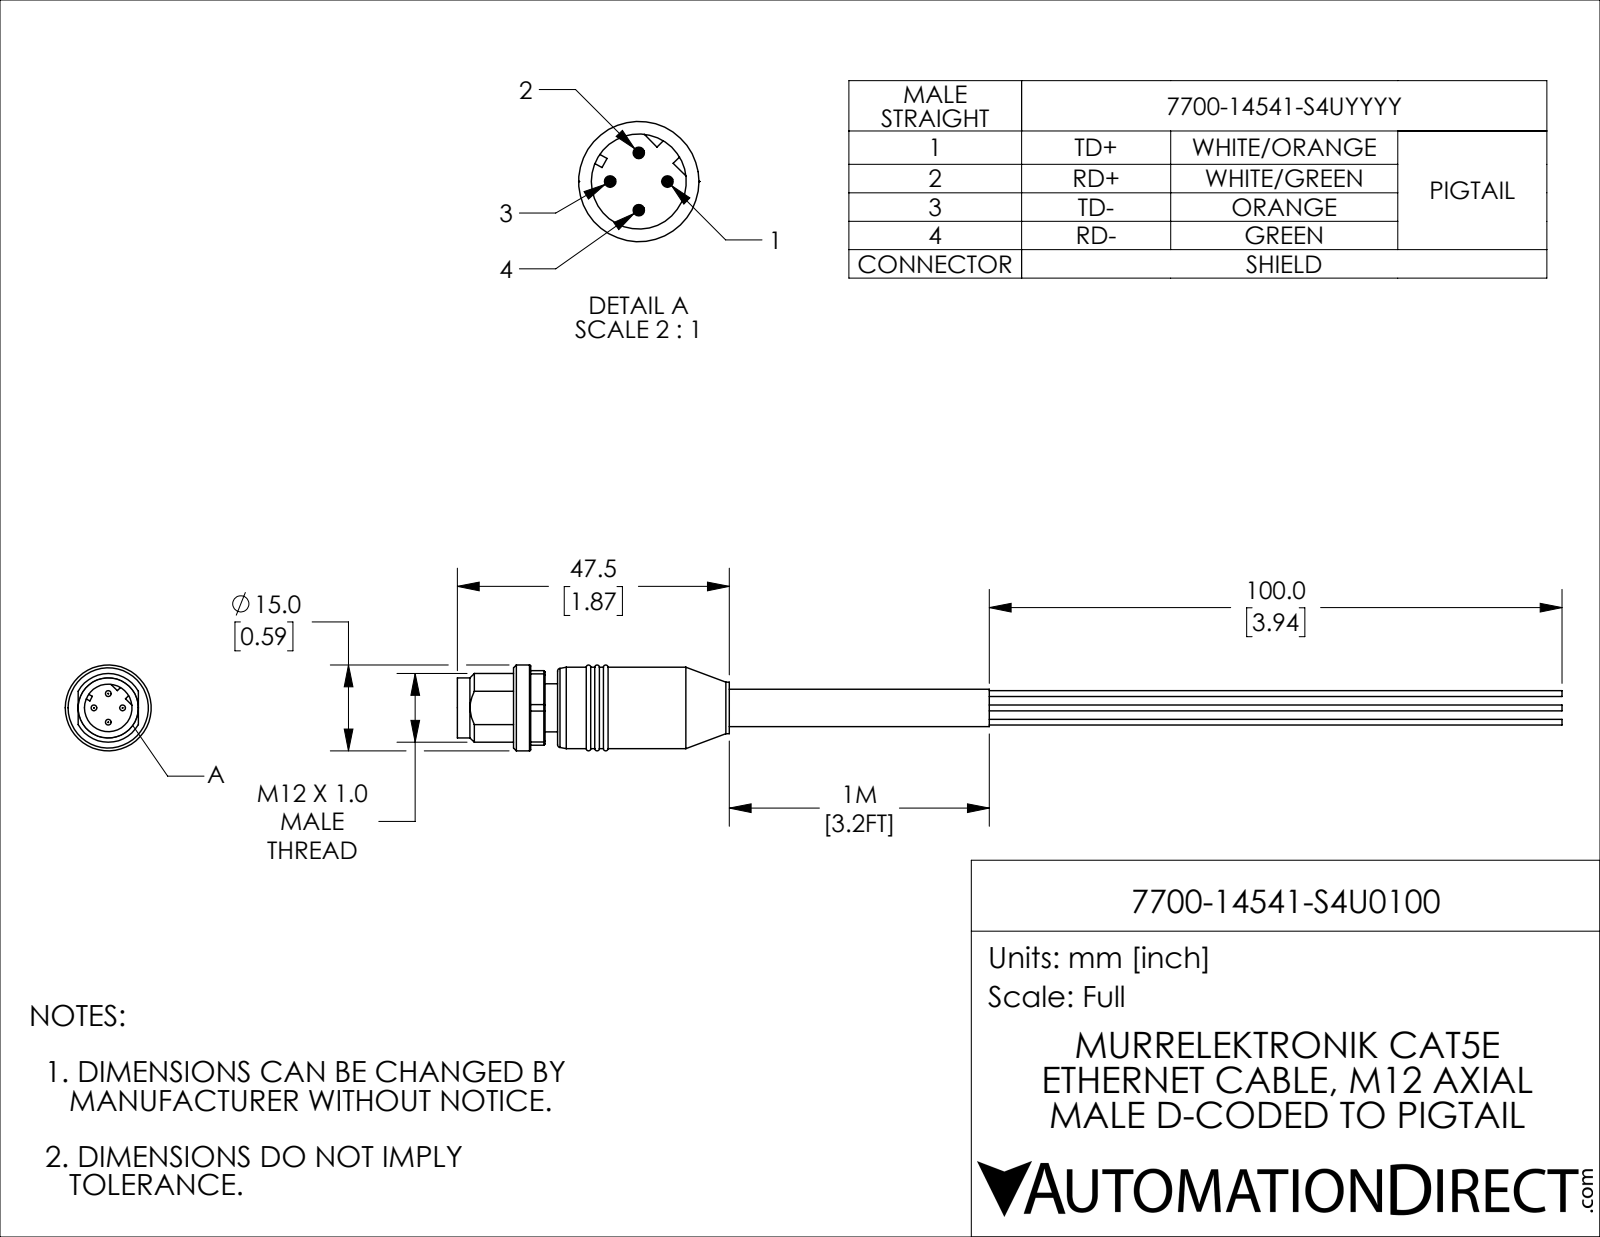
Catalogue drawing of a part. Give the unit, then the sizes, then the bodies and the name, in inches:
Units: inches
Overall size (bounding box): 7.594 × 0.591 × 0.591
Round holes (diameter × count): ⌀0.327 ×1
Round bosses / shafts (diameter × count): ⌀0.039 ×4, ⌀0.591 ×1, ⌀0.559 ×1, ⌀0.413 ×1, ⌀0.354 ×1, ⌀0.331 ×1, ⌀0.256 ×1
Partial cylindrical surfaces — rounded edges, fillets, slot ends (radius × count): R0.236 ×1, R0.283 ×1
Main face-to-face distances: 0.087, 0.035, 0.252, 0.339, 0.217, 0.303, 0.512, 0.413, 0.35, 0.386
Volume: 0.473 in³ · Surface area: 7.675 in²
Bodies: 1 solid, 125 faces (40 planar, 45 cylindrical, 40 other)
Part name (STEP PRODUCT): 7700-14541-S4U0100
STEP written by: SolidWorks 2021 (CONFIG_CONTROL_DESIGN)
